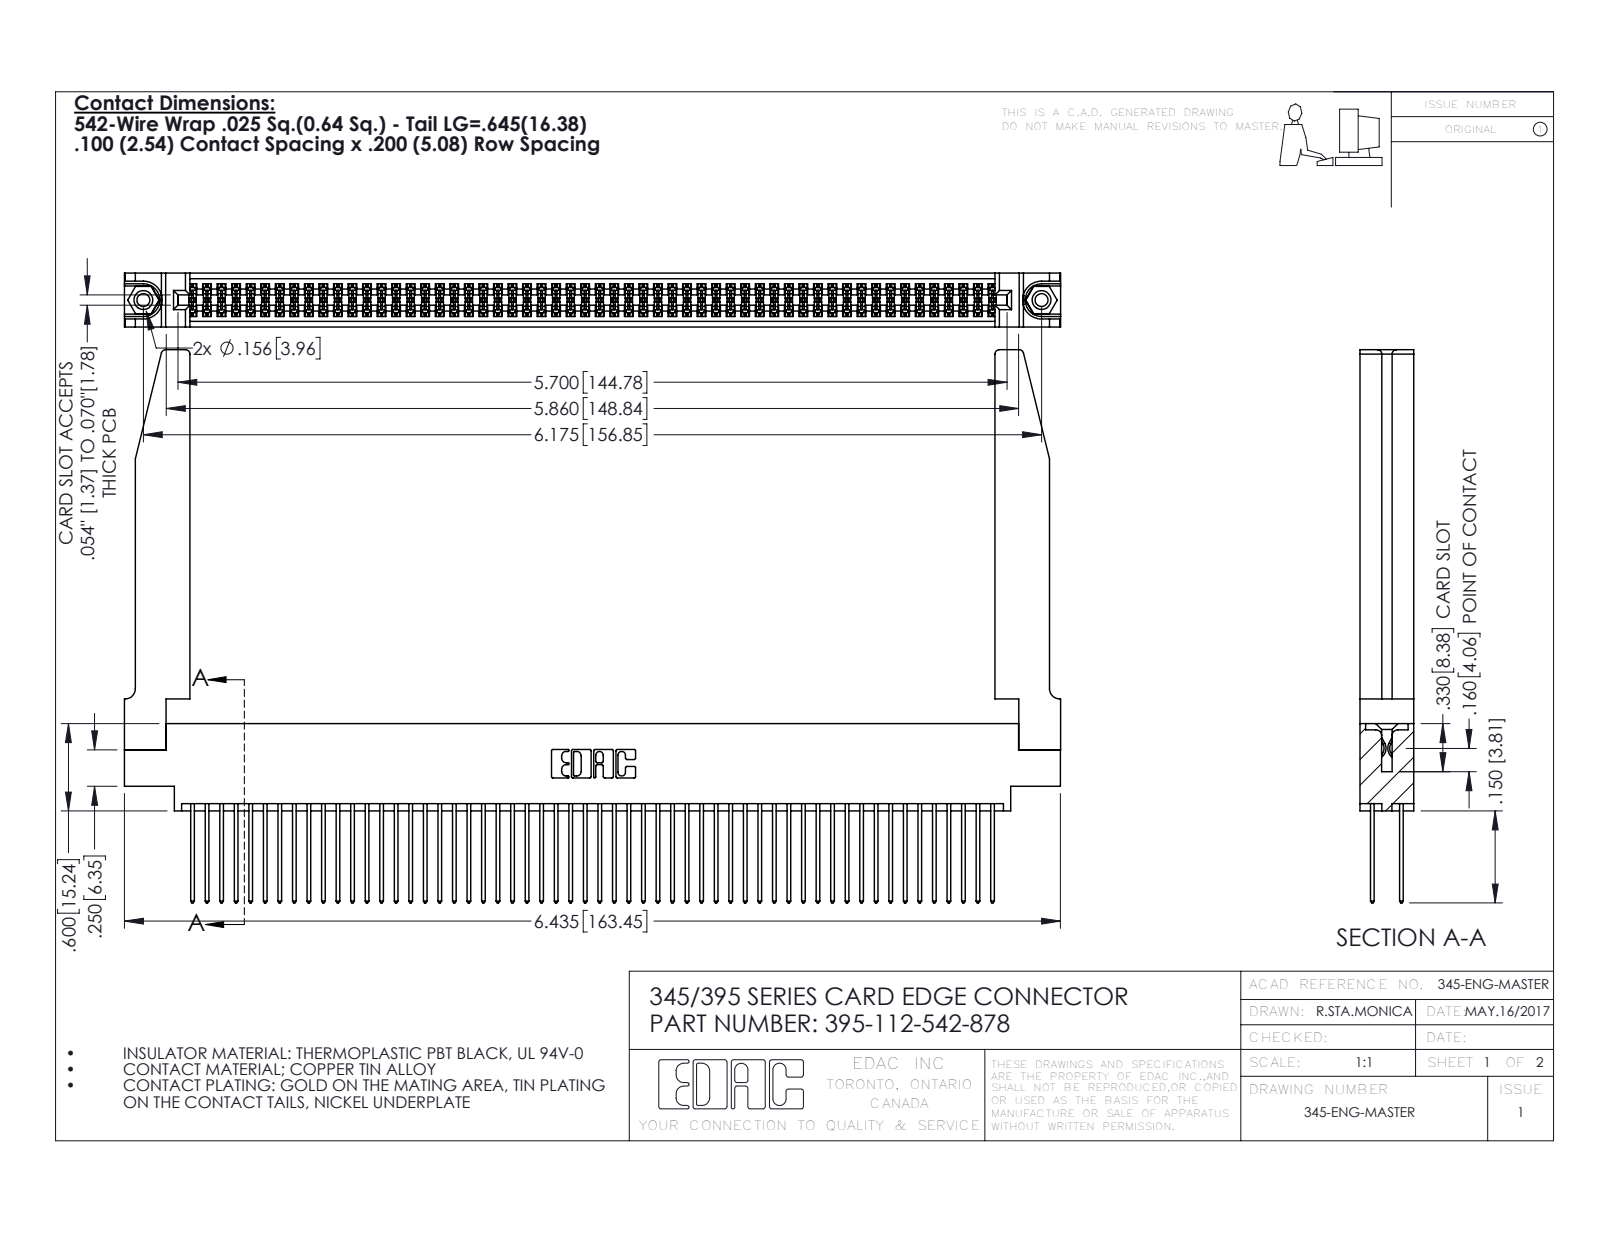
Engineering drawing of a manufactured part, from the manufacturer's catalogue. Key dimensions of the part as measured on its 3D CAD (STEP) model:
Part name (STEP PRODUCT): 345-250-001_345-250-001-102; 345-292-001_345-293-142; 345-220-078_345-220-078; 345 Part_0.170 Offset - 0.156 Dia-TH (+1 more)
STEP written by: SolidWorks 2016 (CONFIG_CONTROL_DESIGN)
Units: inches
Bodies: 117 solids, 5964 faces (3922 planar, 1990 cylindrical, 52 other)
Overall size (bounding box): 6.436 × 3.802 × 0.37
Volume: 1.476 in³ · Surface area: 52.64 in²
Round holes (diameter × count): ⌀0.089 ×2, ⌀0.125 ×2, ⌀0.156 ×2, ⌀0.064 ×1
Round bosses / shafts (diameter × count): ⌀0.155 ×2
Partial cylindrical surfaces — rounded edges, fillets, slot ends (radius × count): R0.006 ×168, R0.01 ×112, R0.01 ×22, R0.03 ×8, R0.007 ×6, R0.031 ×6, R0.026 ×3, R0.014 ×2
Main face-to-face distances: 0.072, 0.298, 0.37, 0.098, 0.272, 0.025, 0.2, 0.225, 0.175, 0.148
Hole centre spacings: 0.27, 5.939, 6.175
